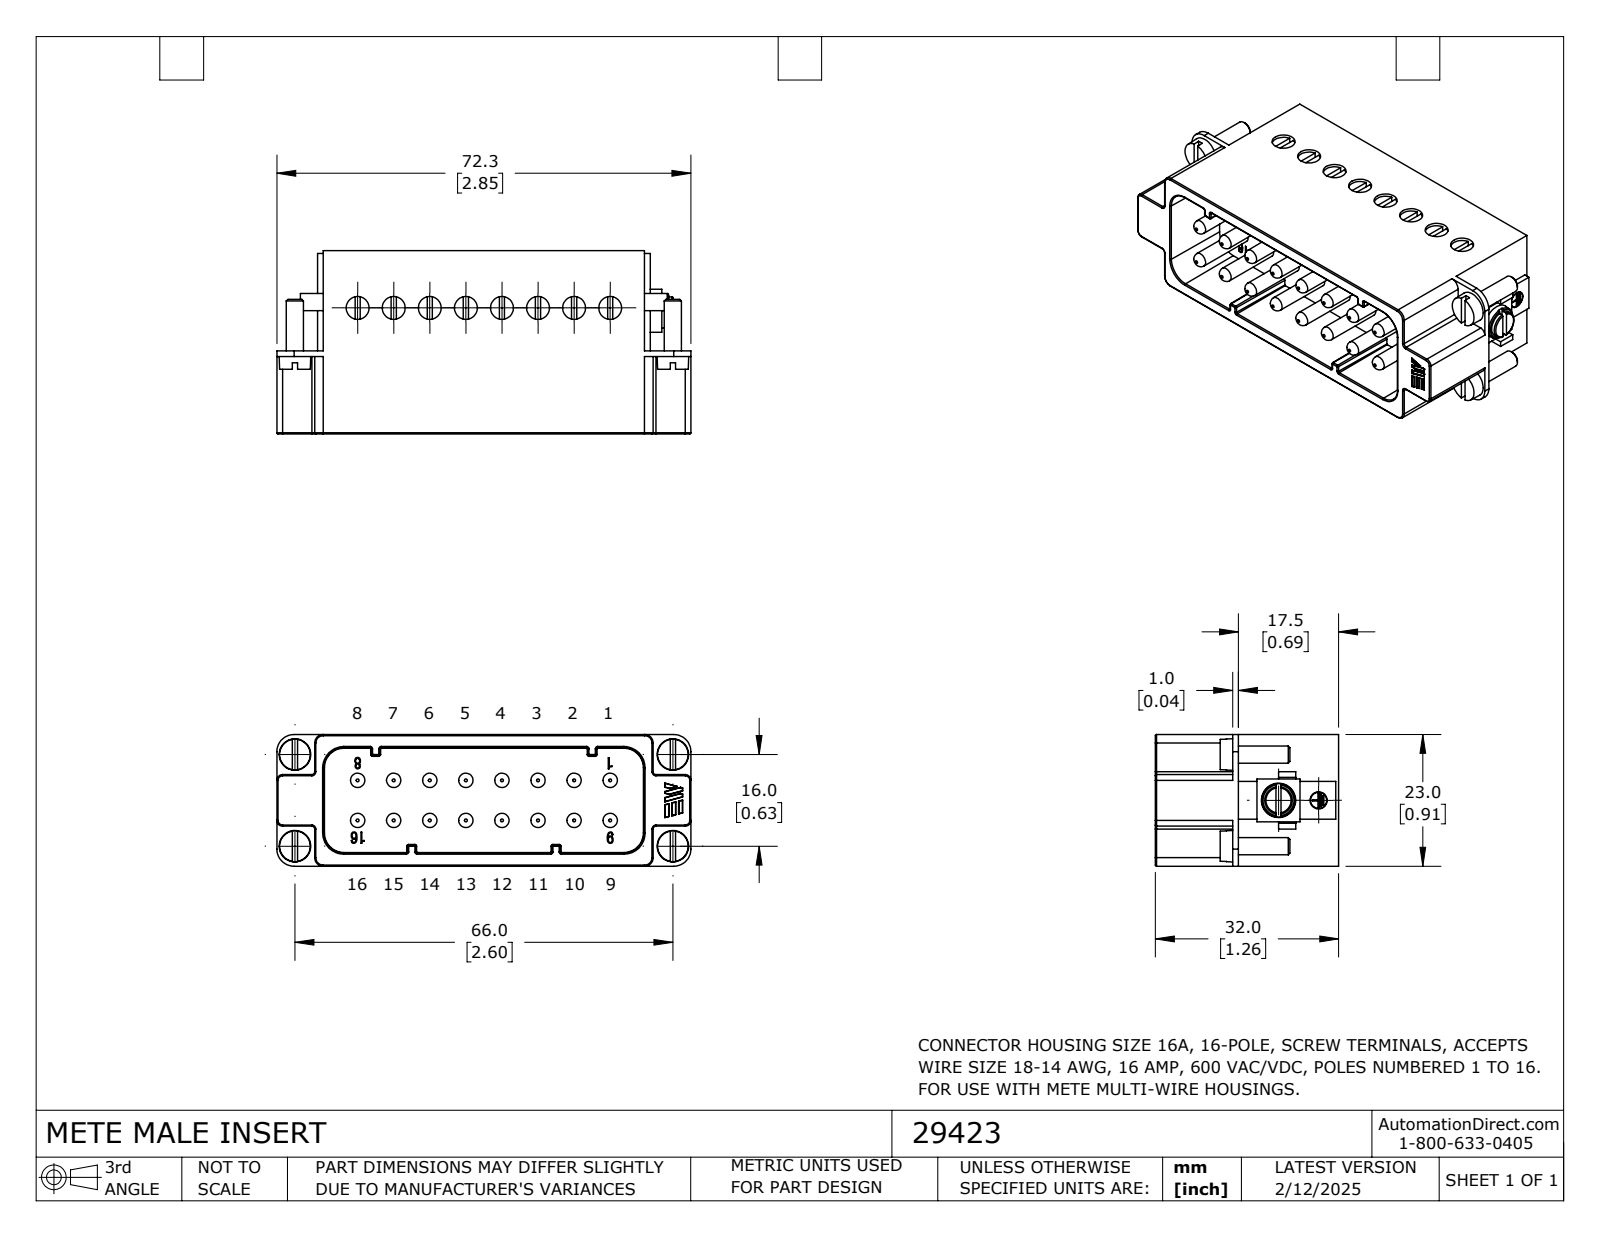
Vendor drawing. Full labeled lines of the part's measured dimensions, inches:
Part name (STEP PRODUCT): 29423
STEP written by: SolidWorks 2024 (CONFIG_CONTROL_DESIGN)
Units: inches
Bodies: 1 solid, 630 faces (303 planar, 186 cylindrical, 141 other)
Overall size (bounding box): 2.846 × 1.26 × 0.906
Volume: 1.874 in³ · Surface area: 24.83 in²
Round holes (diameter × count): ⌀0.157 ×24, ⌀0.118 ×1
Round bosses / shafts (diameter × count): ⌀0.098 ×16, ⌀0.118 ×4, ⌀0.189 ×1, ⌀0.11 ×1
Partial cylindrical surfaces — rounded edges, fillets, slot ends (radius × count): R0.008 ×22, R0.02 ×4, R0.039 ×4, R0.059 ×4, R0.118 ×4
Main face-to-face distances: 0.906, 0.787, 0.098, 0.02, 0.472, 0.059, 1.26, 0.276, 0.571, 0.689
Hole centre spacings: 0.248, 0.496, 0.744, 0.371, 0.567, 0.992, 0.793, 1.24
